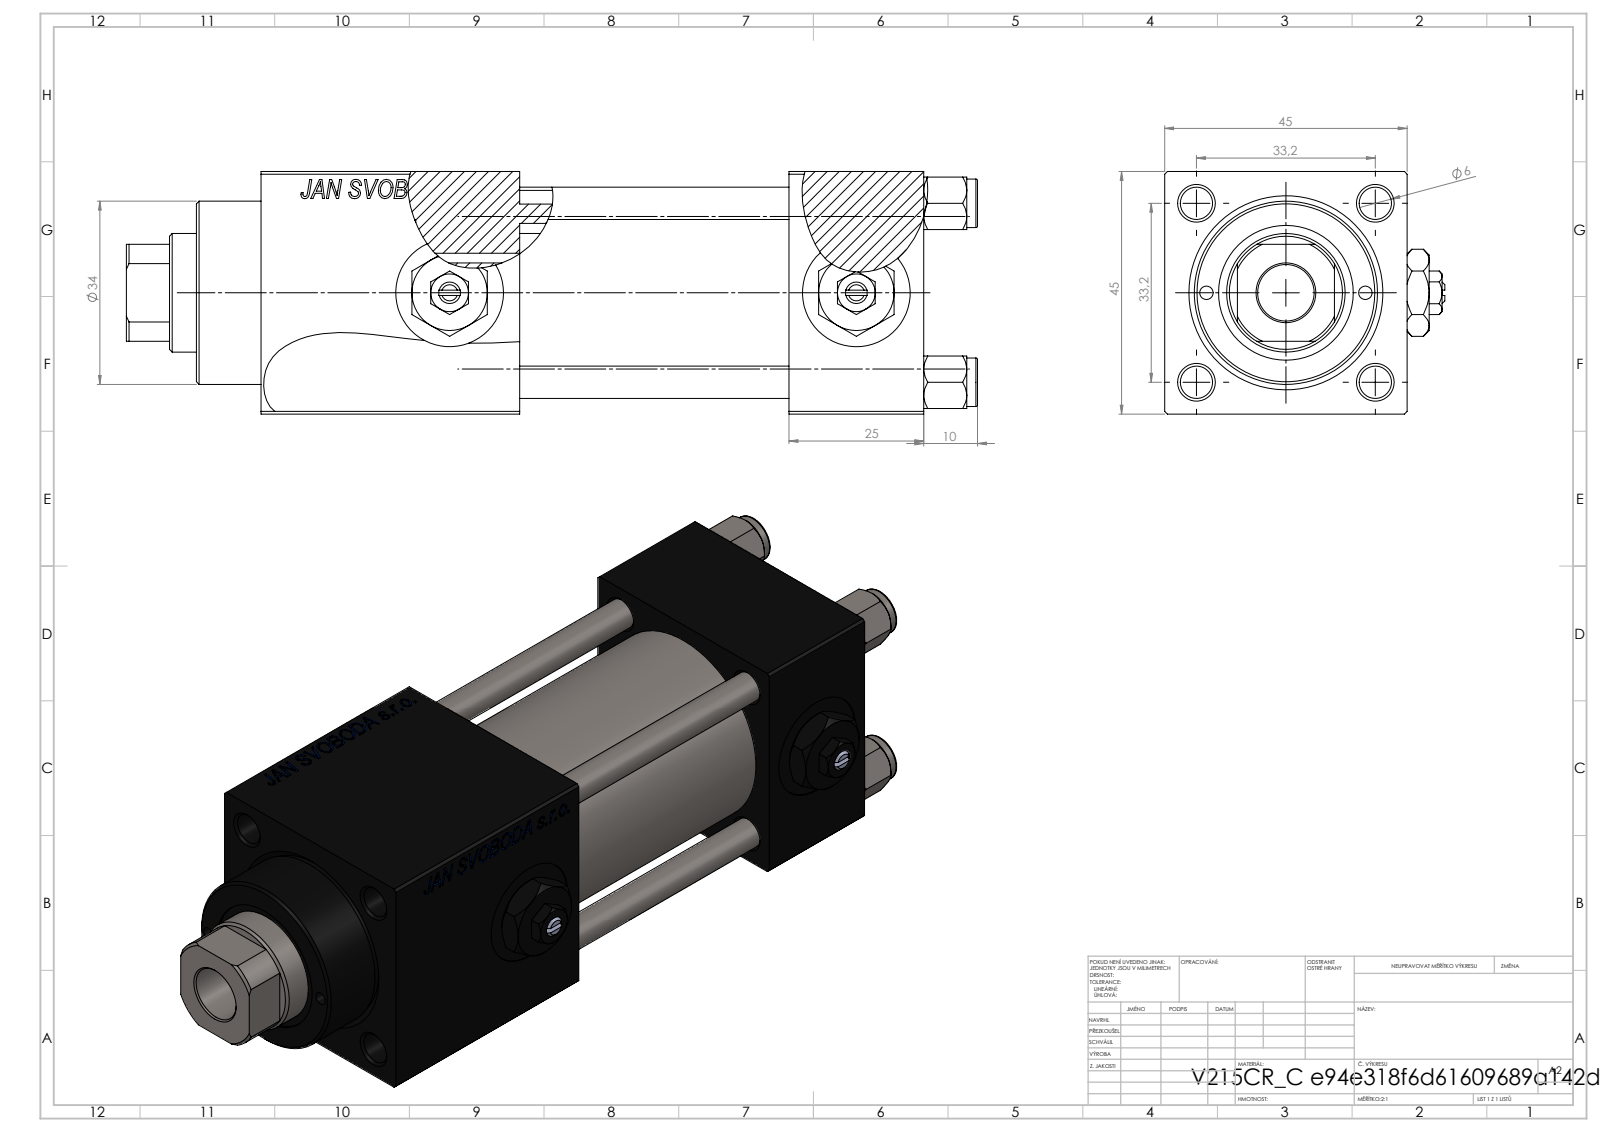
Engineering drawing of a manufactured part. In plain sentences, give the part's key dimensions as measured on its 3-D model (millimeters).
The part is named "V215CR_C_Body; NUT_M5_C; V215_VC_A; Zatka_pro_OIL_PORT (+2 more)". Its 3-D file was written by "SolidWorks 2019 (CONFIG_CONTROL_DESIGN)". It is 12 solids with 1254 faces: 574 planar, 102 cylindrical and 578 other. Overall it measures 158 by 52 by 45 millimeters. Its volume is 90 998 cubic millimeters and its surface area 73 410 square millimeters. Round holes: 4 of diameter 6, 2 of diameter 2.5, 2 of diameter 7, 2 of diameter 13.16, 2 of diameter 20, 1 of diameter 10.5, 1 of diameter 22, 1 of diameter 24, 1 of diameter 25, 1 of diameter 32, 1 of diameter 33. Round bosses or shafts: 4 of diameter 9, 1 of diameter 38, 1 of diameter 34. Partial cylindrical surfaces (rounded edges, fillets, slot ends): 1 of radius 10.5. The main face-to-face distances are 45, 25, 50, 123, 75, 98, 44.8, 48, 94.3, 69.3. The hole center spacings are 16.7, 23.48, 33.2, 35.47, 14.75, 46.95, 29.5, 75.5.
